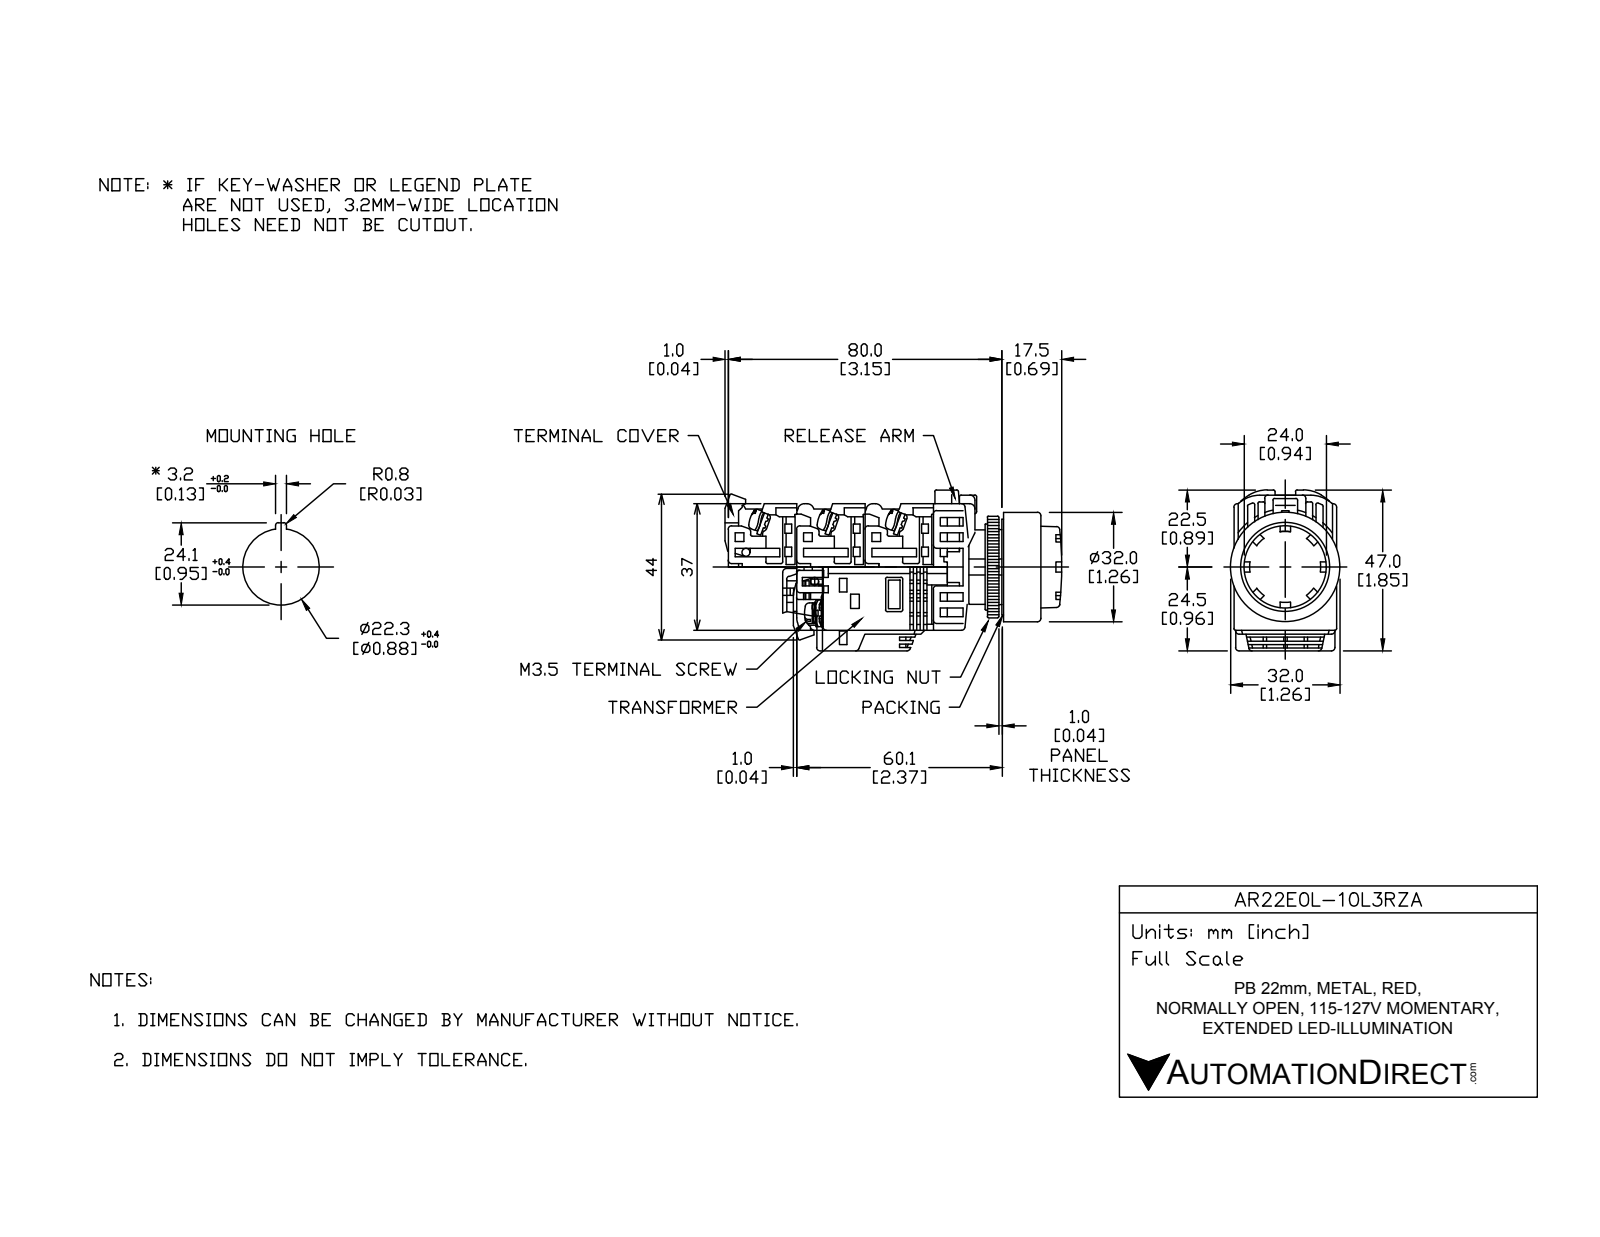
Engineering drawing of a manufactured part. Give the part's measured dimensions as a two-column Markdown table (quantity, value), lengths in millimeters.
| quantity | value |
| --- | --- |
| part name | AR22E0L-10L3RZA |
| STEP written by | SolidWorks 2017 (AUTOMOTIVE_DESIGN) |
| units | millimeters |
| bodies | 16 solids, 451 faces (317 planar, 99 cylindrical, 35 other) |
| overall size | 79.25 × 43.81 × 32 |
| volume | 50 413 mm³ |
| surface area | 26 207 mm² |
| round holes (diameter × count) | 21.8 × 1, 22 × 1, 25 × 1, 31 × 1 |
| round bosses / shafts (diameter × count) | 5 × 4, 32 × 1, 30.5 × 1, 29.8 × 1, 24 × 1, 23.8 × 1, 21.75 × 1, 17 × 1 |
| partial cylindrical surfaces (radius × count) | 0.5 × 32, 1.75 × 8, 5 × 4, 4 × 2, 16.59 × 1, 17.59 × 1 |
| main face-to-face distances | 1, 18, 29, 20, 28.5, 3, 2, 21, 0.35, 7.5 |
